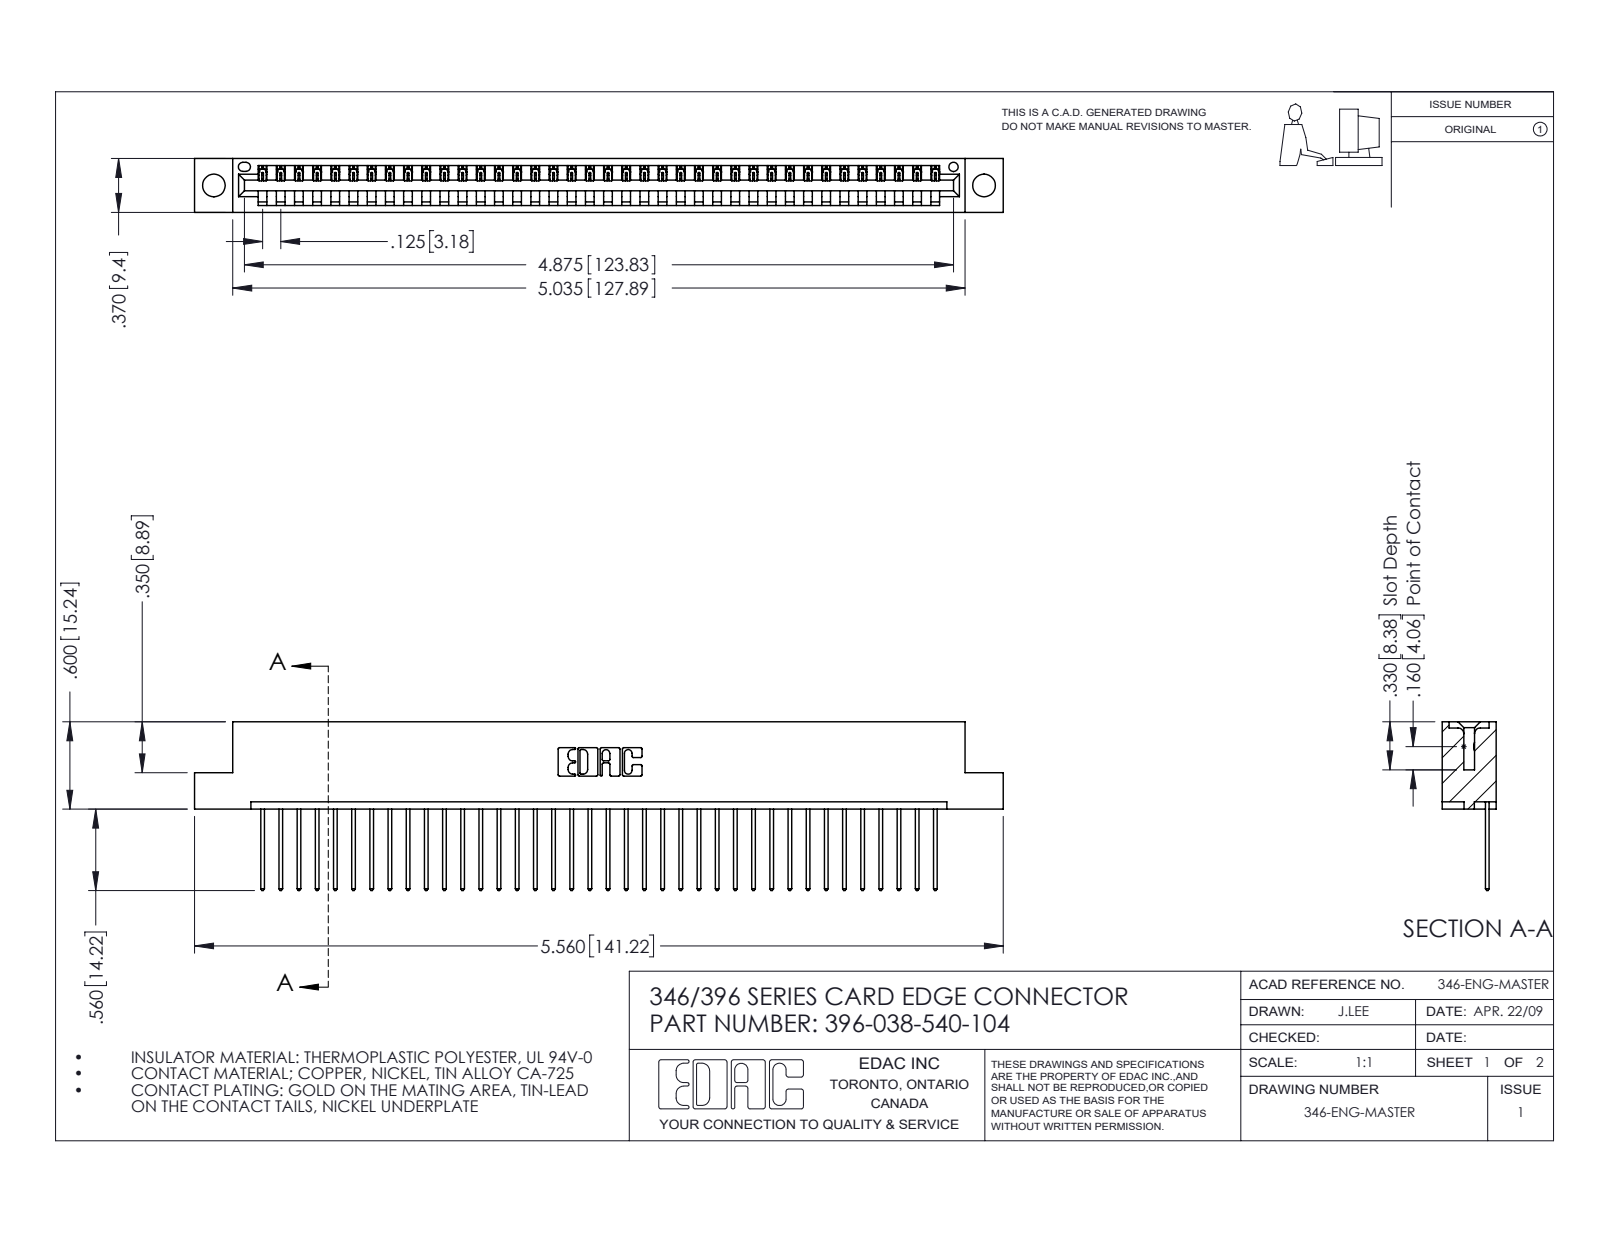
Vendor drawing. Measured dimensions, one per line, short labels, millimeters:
name: 345-292-001_345-293-140; 396-038-540-104; 346 Part_Flush Mounting Lugs - 0.156 Dia-TH
written by: SolidWorks 2016 (CONFIG_CONTROL_DESIGN)
unit: mm
bodies: 39 solids, 2326 faces (1596 planar, 730 cylindrical, 0 other)
size: 141.2 × 29.5 × 9.4
volume: 13 500 mm³; area: 16 950 mm²
holes: 2× ⌀4, 1× ⌀1.6
rounds: 76× R0.2, 76× R0.3, 22× R0.3, 6× R0.2, 6× R0.8, 3× R0.7, 2× R0.8, 2× R1
face distances: 1.2, 8.2, 9.4, 6.4, 1.8, 7.6, 0.6, 3.8, 5.6, 2.5
hole spacings: 6.2, 129.2, 134.5
